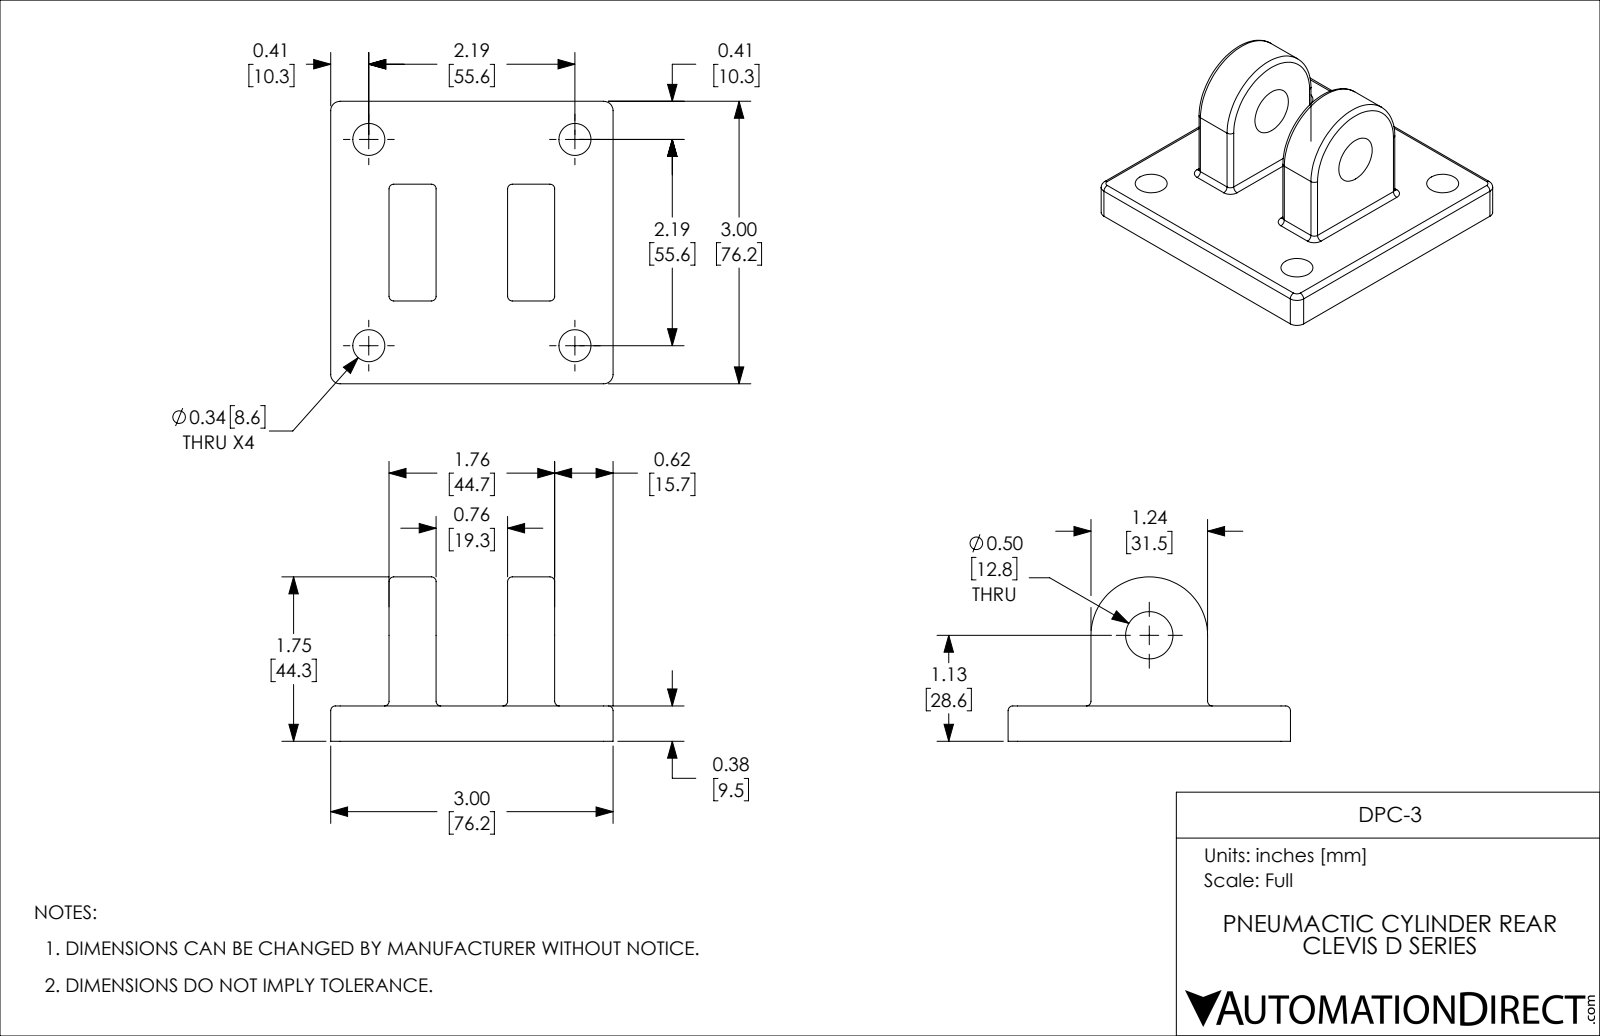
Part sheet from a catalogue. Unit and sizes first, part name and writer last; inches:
Units: inches
Overall size (bounding box): 3 × 3 × 1.745
Round holes (diameter × count): ⌀0.34 ×4, ⌀0.502 ×1
Partial cylindrical surfaces — rounded edges, fillets, slot ends (radius × count): R0.05 ×20, R0.1 ×4, R0.62 ×1
Main face-to-face distances: 0.375, 0.5, 1.26, 0.62, 1.12, 1.88, 2.38, 3, 0.88, 2.12
Hole centre spacings: 2.19, 3.097
Volume: 4.562 in³ · Surface area: 31.73 in²
Bodies: 1 solid, 71 faces (14 planar, 39 cylindrical, 18 other)
Part name (STEP PRODUCT): DPC-3
STEP written by: SolidWorks 2018 (AUTOMOTIVE_DESIGN)
